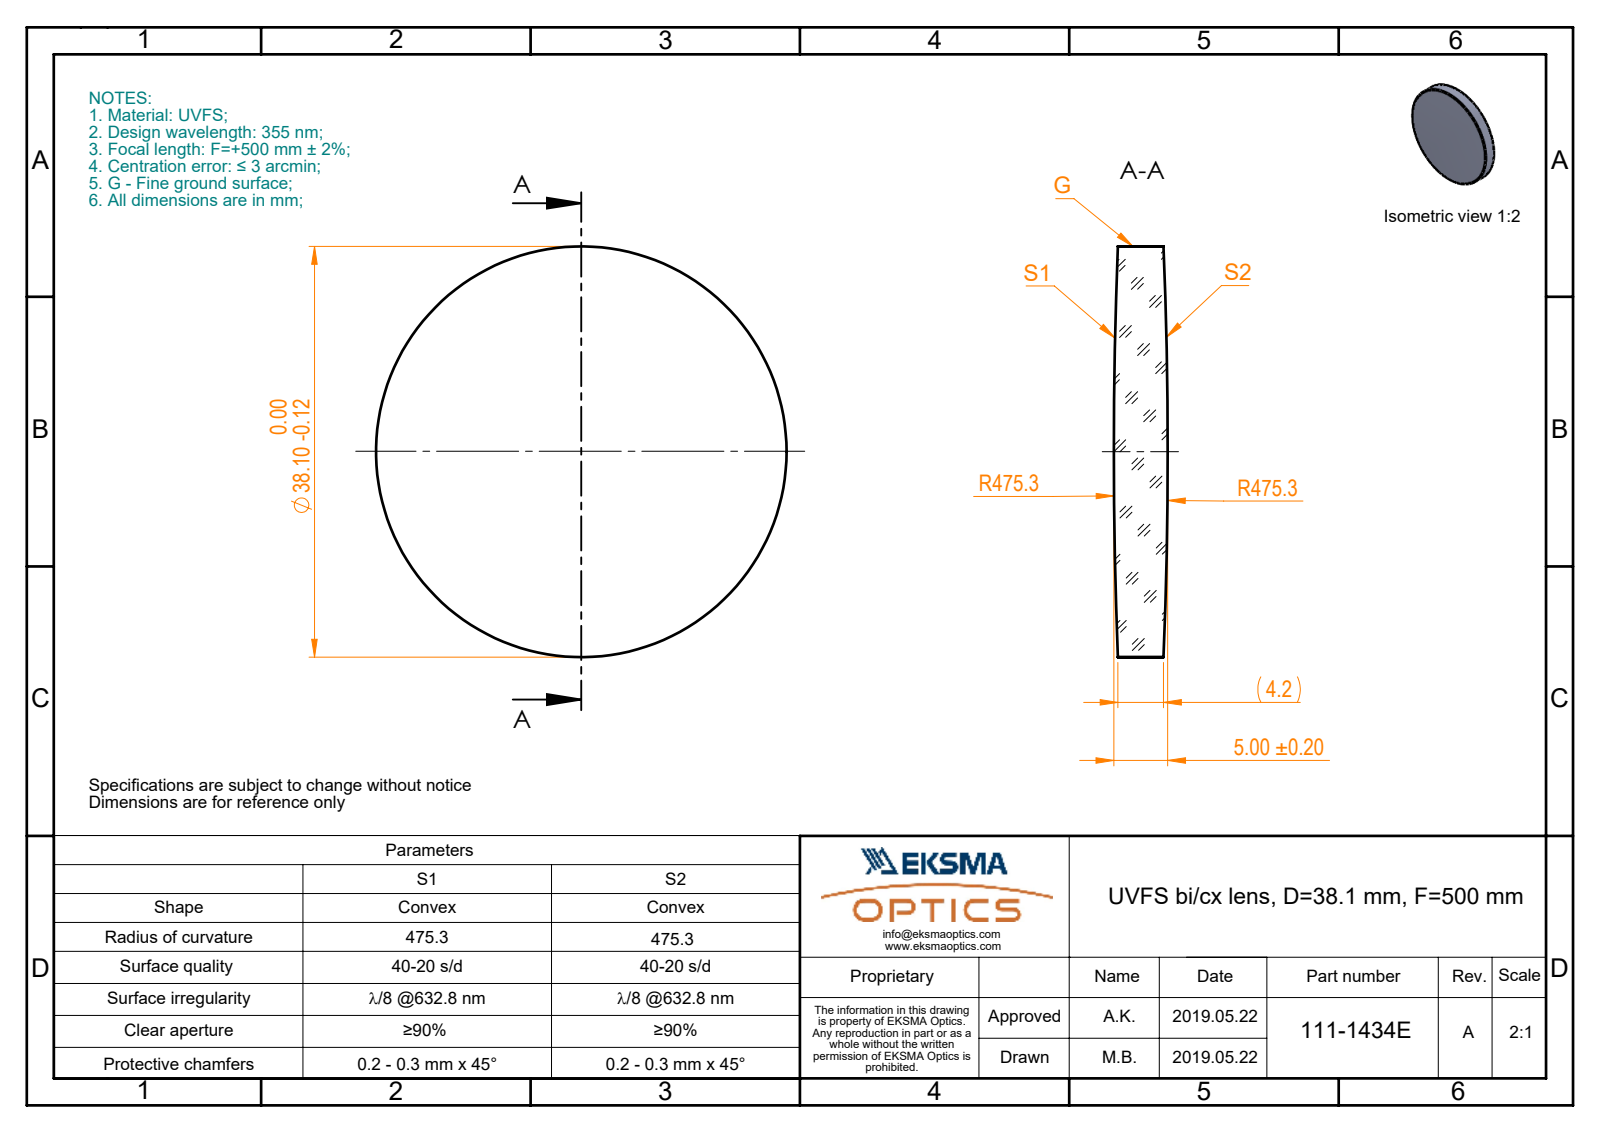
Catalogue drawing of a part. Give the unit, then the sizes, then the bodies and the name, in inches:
Units: inches
Overall size (bounding box): 1.5 × 1.5 × 0.197
Round bosses / shafts (diameter × count): ⌀1.5 ×1
Volume: 0.321 in³ · Surface area: 4.321 in²
Bodies: 1 solid, 6 faces (0 planar, 2 cylindrical, 4 other)
Part name (STEP PRODUCT): 111-1434E UVFS bi-cx 38.1 F500
STEP written by: SolidWorks 2017 (CONFIG_CONTROL_DESIGN)
